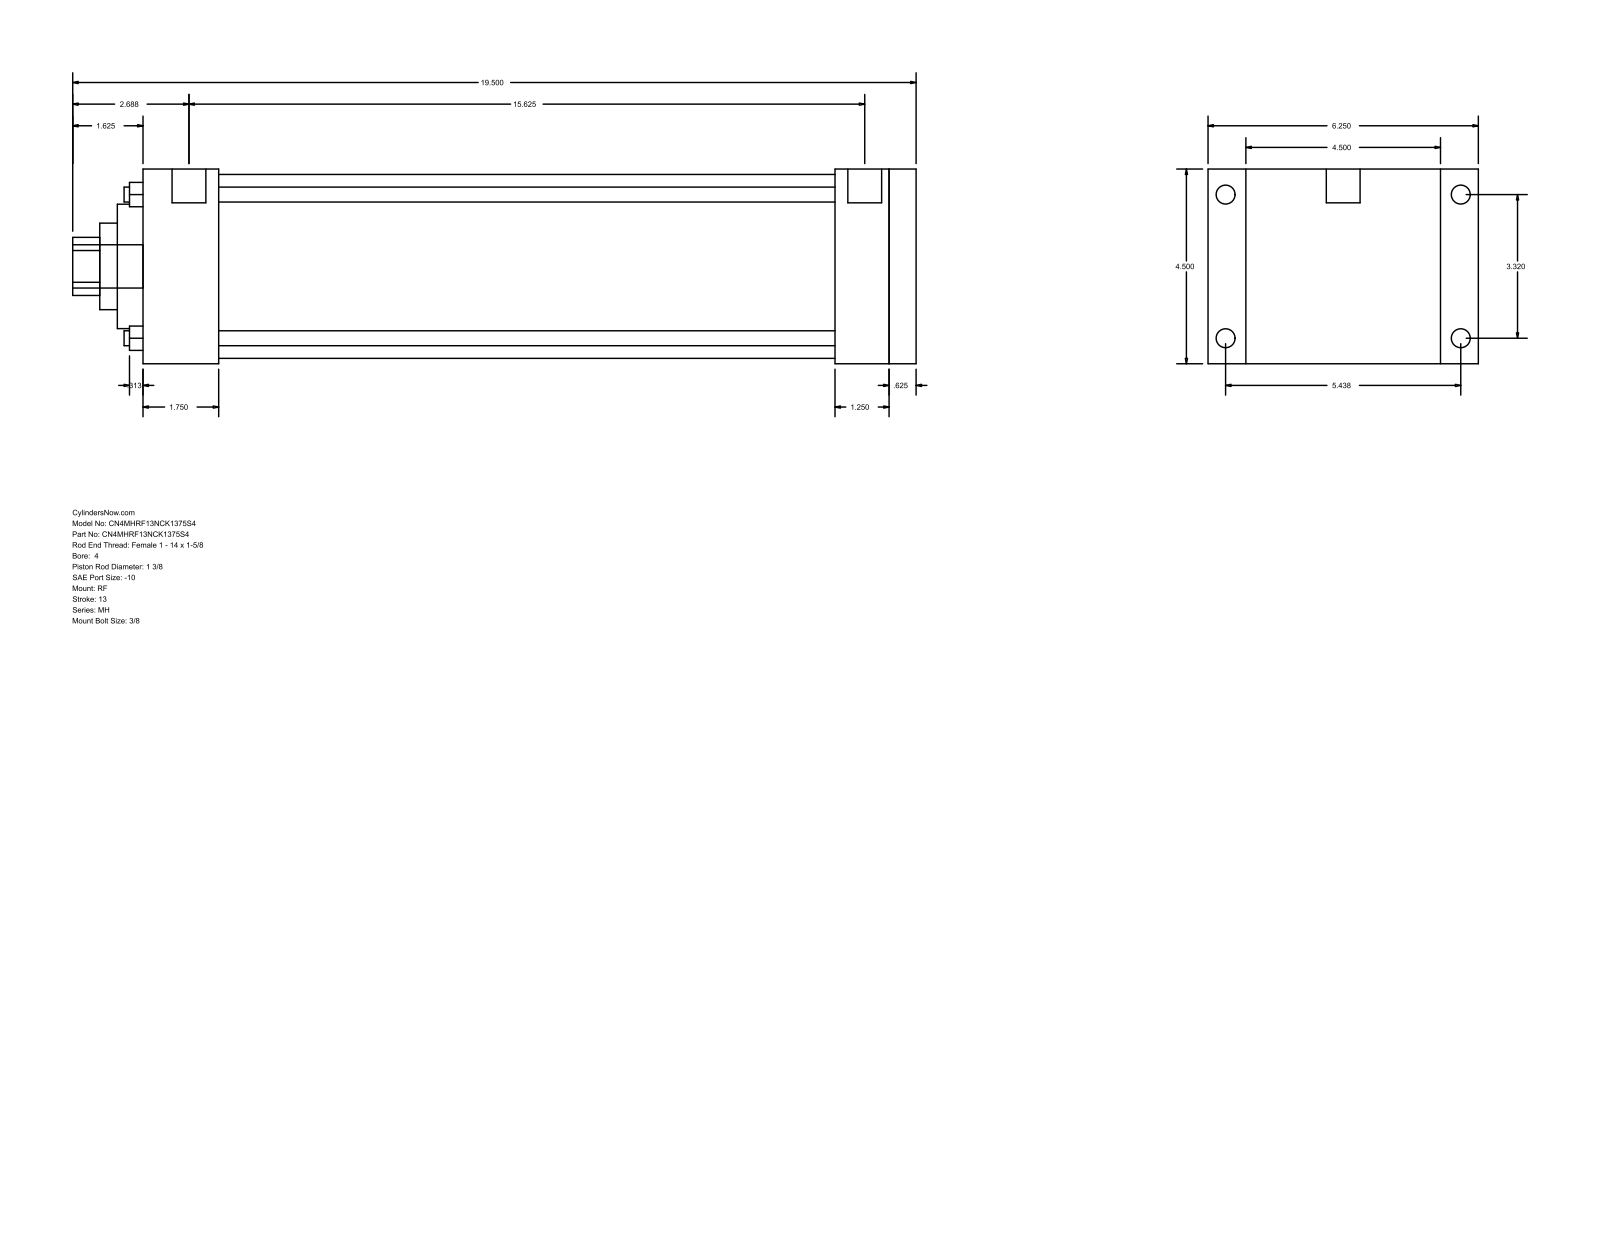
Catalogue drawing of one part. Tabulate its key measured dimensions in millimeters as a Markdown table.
| quantity | value |
| --- | --- |
| part name | MH_RF__0400_1.375 |
| STEP written by | GSSL Pune (CONFIG_CONTROL_DESIGN) |
| units | millimeters |
| bodies | 0 solids, 94 faces (65 planar, 29 cylindrical, 0 other) |
| overall size | 495.3 × 158.75 × 114.3 |
| round holes (diameter × count) | 8.76 × 4, 34.92 × 1, 50.8 × 1, 73.03 × 1, 107.95 × 1 |
| round bosses / shafts (diameter × count) | 11.13 × 4, 8.73 × 4, 19.84 × 2, 25.4 × 1 |
| partial cylindrical surfaces (radius × count) | 17.06 × 1 |
| main face-to-face distances | 114.3, 454.03, 438.16, 15.87, 44.45, 393.71, 409.58, 406.41, 361.96, 31.75 |
| hole center spacings | 59.62, 84.32, 119.25 |
